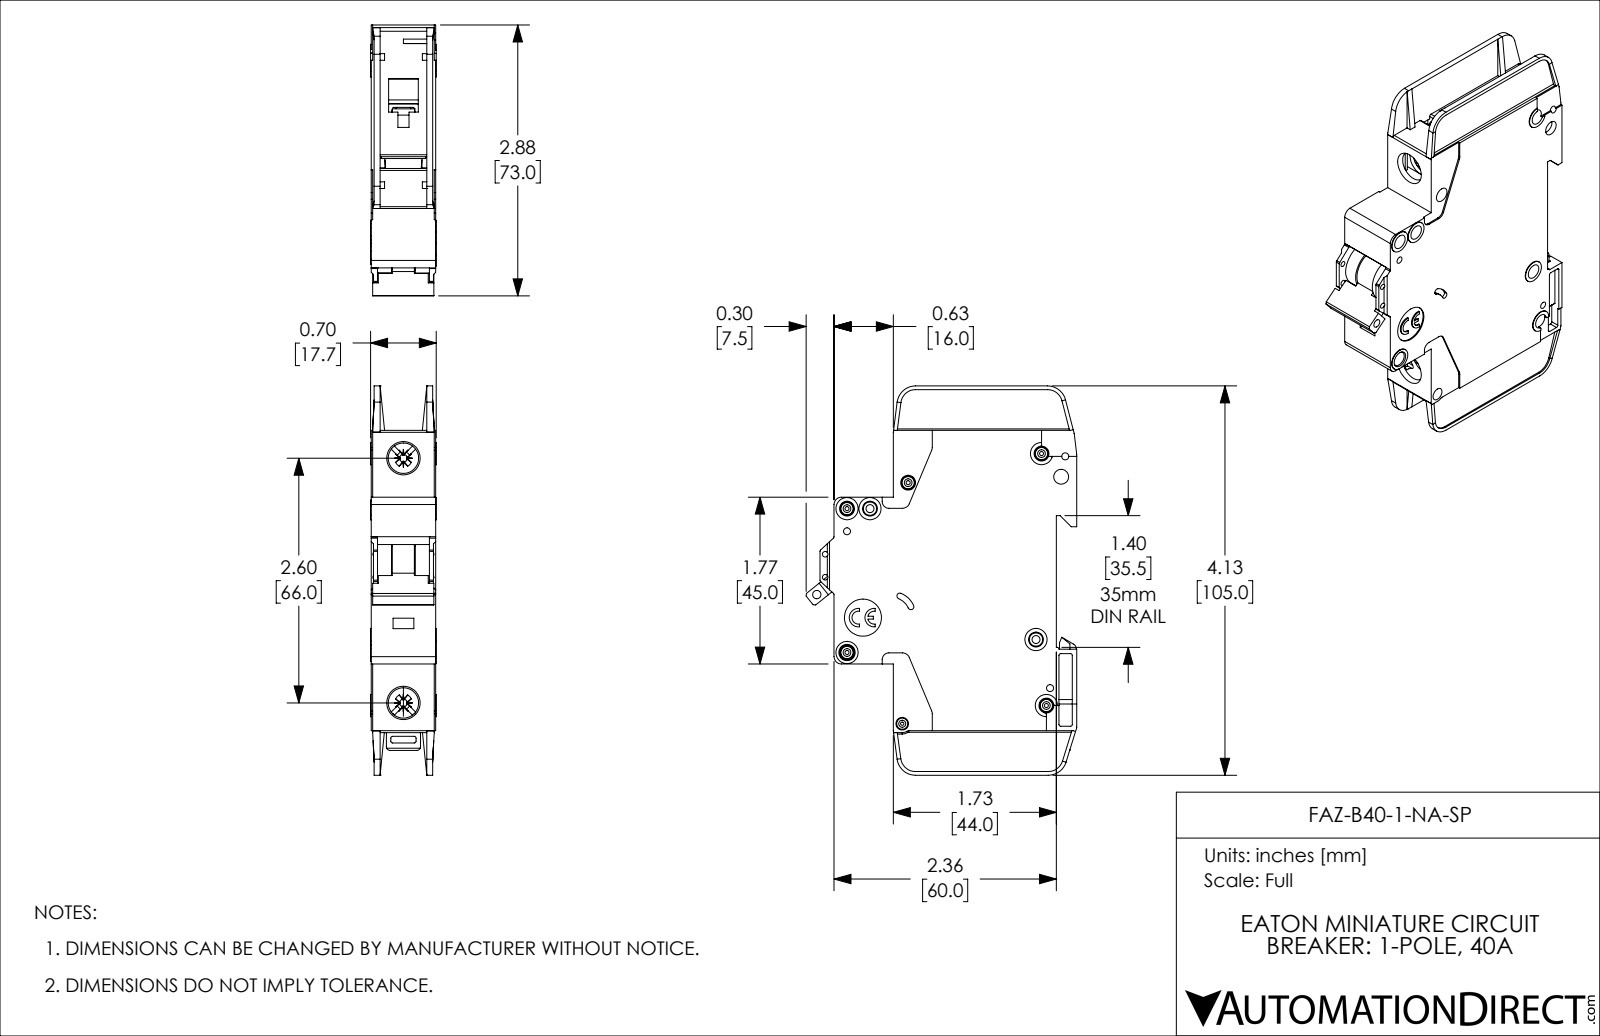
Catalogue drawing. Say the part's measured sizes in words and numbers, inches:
The part is named "FAZ-B40-1-NA-SP". Its 3-D file was written by "SolidWorks 2019 (AUTOMOTIVE_DESIGN)". It is 1 solid with 1127 faces: 671 planar, 357 cylindrical and 99 other. Overall it measures 4.134 by 2.876 by 0.697 inches. Its volume is 4.682 cubic inches and its surface area 41.01 square inches. Round holes: 8 of diameter 0.157, 5 of diameter 0.043, 4 of diameter 0.075, 2 of diameter 0.059, 2 of diameter 0.085, 2 of diameter 0.323, 1 of diameter 0.035, 1 of diameter 0.089, 1 of diameter 0.098, 1 of diameter 0.134, 1 of diameter 0.394. Round bosses or shafts: 5 of diameter 0.13, 4 of diameter 0.236, 2 of diameter 0.118, 1 of diameter 0.098. Partial cylindrical surfaces (rounded edges, fillets, slot ends): 42 of radius 0.02, 10 of radius 0.016, 10 of radius 0.039, 8 of radius 0.079, 5 of radius 0.197, 4 of radius 0.008, 4 of radius 0.026, 4 of radius 0.043. The main face-to-face distances are 0.047, 0.685, 0.591, 0.638, 0.094, 0.543, 0.016, 0.031, 0.496, 0.575. The hole center spacings are 0.244, 0.537, 0.87, 0.189, 0.199, 0.204, 0.221, 0.24.
